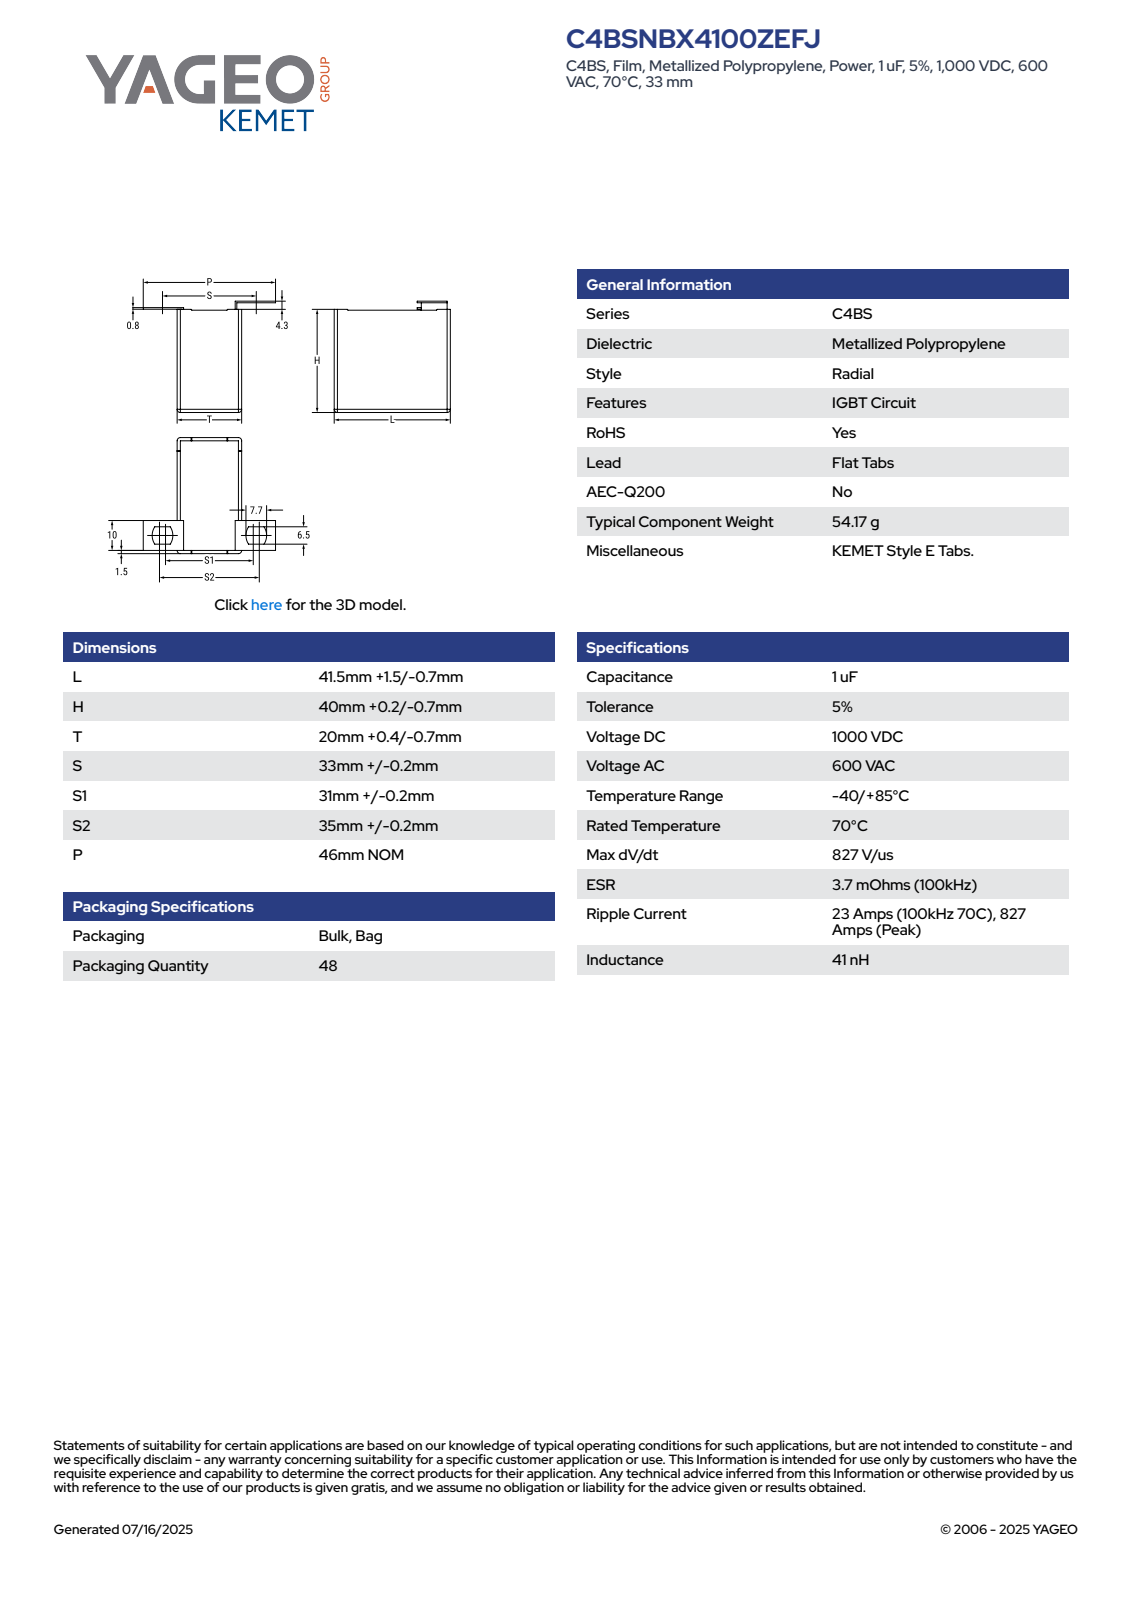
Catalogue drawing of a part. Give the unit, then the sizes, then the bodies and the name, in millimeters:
Units: millimetres
Overall size (bounding box): 46 × 44.51 × 43
Partial cylindrical surfaces — rounded edges, fillets, slot ends (radius × count): R0.4 ×2
Main face-to-face distances: 20.4, 43, 39.2, 0.8, 3.5, 1, 40.2, 0.75, 1.8, 41
Volume: 34 675 mm³ · Surface area: 7 641 mm²
Bodies: 4 solids, 89 faces (83 planar, 2 cylindrical, 4 other)
Part name (STEP PRODUCT): CFP_C4BE_41.5X40X20_L43H40.2T20.4
STEP written by: SolidWorks 2014 (AUTOMOTIVE_DESIGN)
